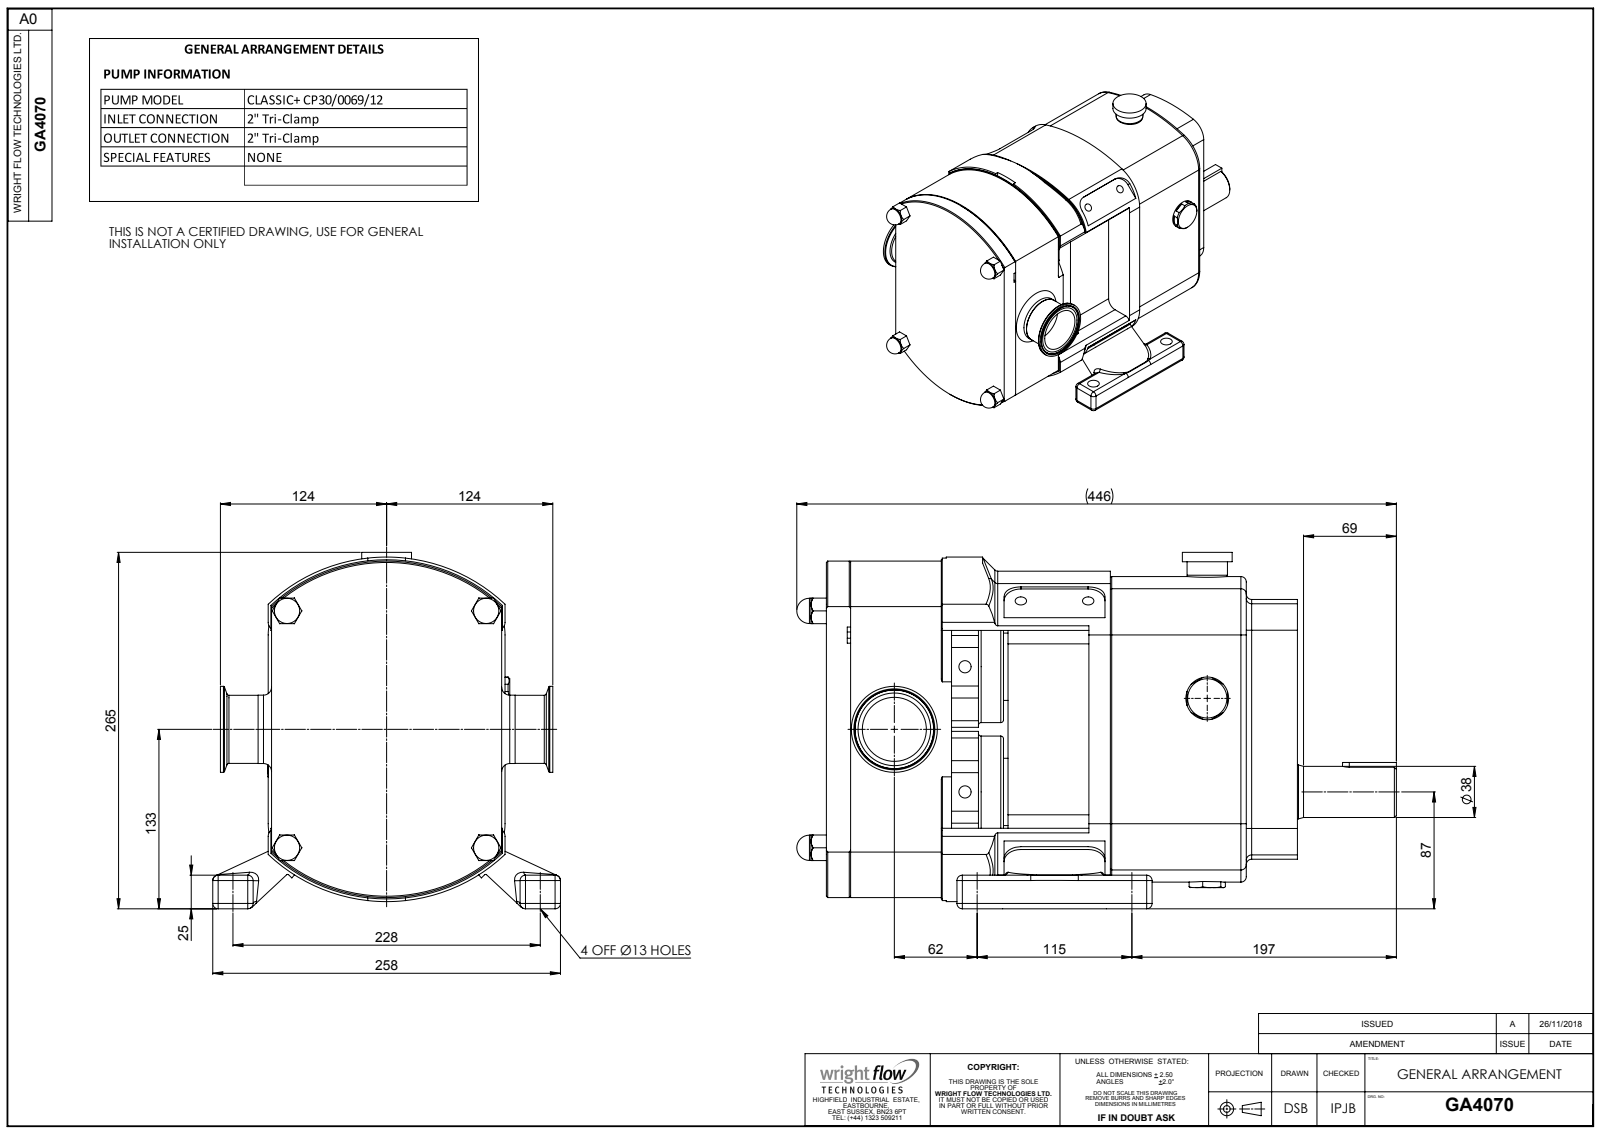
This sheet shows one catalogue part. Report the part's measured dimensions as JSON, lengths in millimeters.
{"part_name": "Copy of Z94-5121-33 - 2 INCH^GA4070; Copy of CP30-0069-12 H B^GA4070; GA4070", "step_written_by": "SolidWorks 2023 (AUTOMOTIVE_DESIGN)", "units": "millimeters", "bodies": {"solids": 3, "faces": 728, "planar": 267, "cylindrical": 238, "other": 223}, "overall_size": [445.58, 264.84, 258.38], "volume_mm3": 11460000, "surface_area_mm2": 523986, "round_holes": [[8.5, 4], [10.11, 4], [13, 4], [9.09, 2], [35, 1], [47.6, 1]], "round_bosses_or_shafts": [[18.8, 4], [83, 2], [50, 2], [63.9, 1], [50.8, 1], [50.6, 1], [40.01, 1], [38, 1]], "partial_cylinders_radius": [[4, 44], [1, 16], [10, 12], [6, 10], [12.5, 4], [12.57, 4], [12.6, 4], [20, 4]], "face_to_face_distances": [1.5, 169.5, 139, 38, 134.98, 29, 215.05, 350.03, 30.5, 140.5], "hole_center_spacings": [63.64, 50.05, 70.13, 90, 115, 127.18, 205.62, 228.38]}
